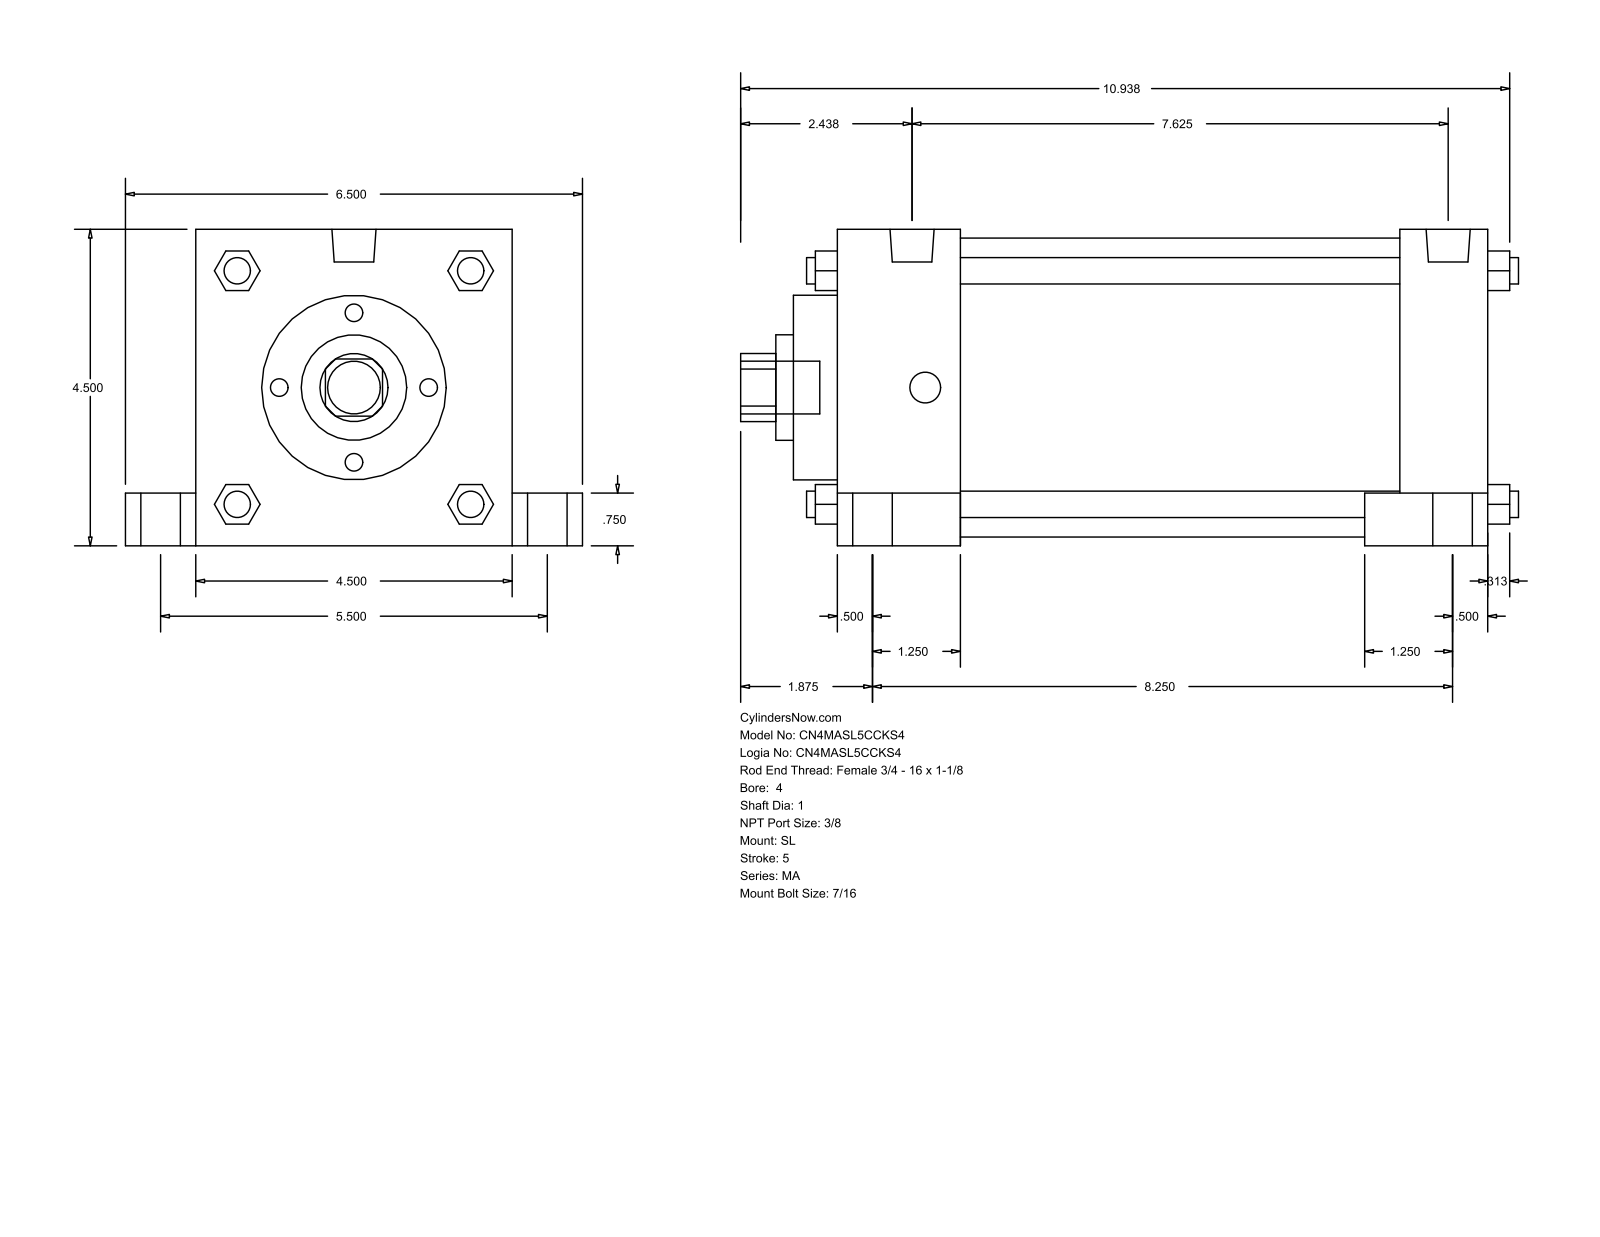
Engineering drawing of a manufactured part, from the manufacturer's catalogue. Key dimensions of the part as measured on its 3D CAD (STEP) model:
Part name (STEP PRODUCT): MA_SL__0400_1
STEP written by: GSSL Pune (CONFIG_CONTROL_DESIGN)
Units: millimetres
Bodies: 0 solids, 150 faces (113 planar, 37 cylindrical, 0 other)
Overall size (bounding box): 280.99 × 165.1 × 114.3
Round holes (diameter × count): ⌀25.4 ×1, ⌀38.1 ×1, ⌀66.67 ×1, ⌀107.95 ×1
Round bosses / shafts (diameter × count): ⌀20.64 ×4, ⌀14.29 ×4, ⌀11.11 ×4, ⌀9.53 ×4, ⌀15.93 ×2, ⌀19.05 ×1
Partial cylindrical surfaces — rounded edges, fillets, slot ends (radius × count): R12.29 ×1
Main face-to-face distances: 114.3, 234.96, 44.46, 190.5, 203.2, 158.74, 31.76, 25.4, 139.7, 19.05
